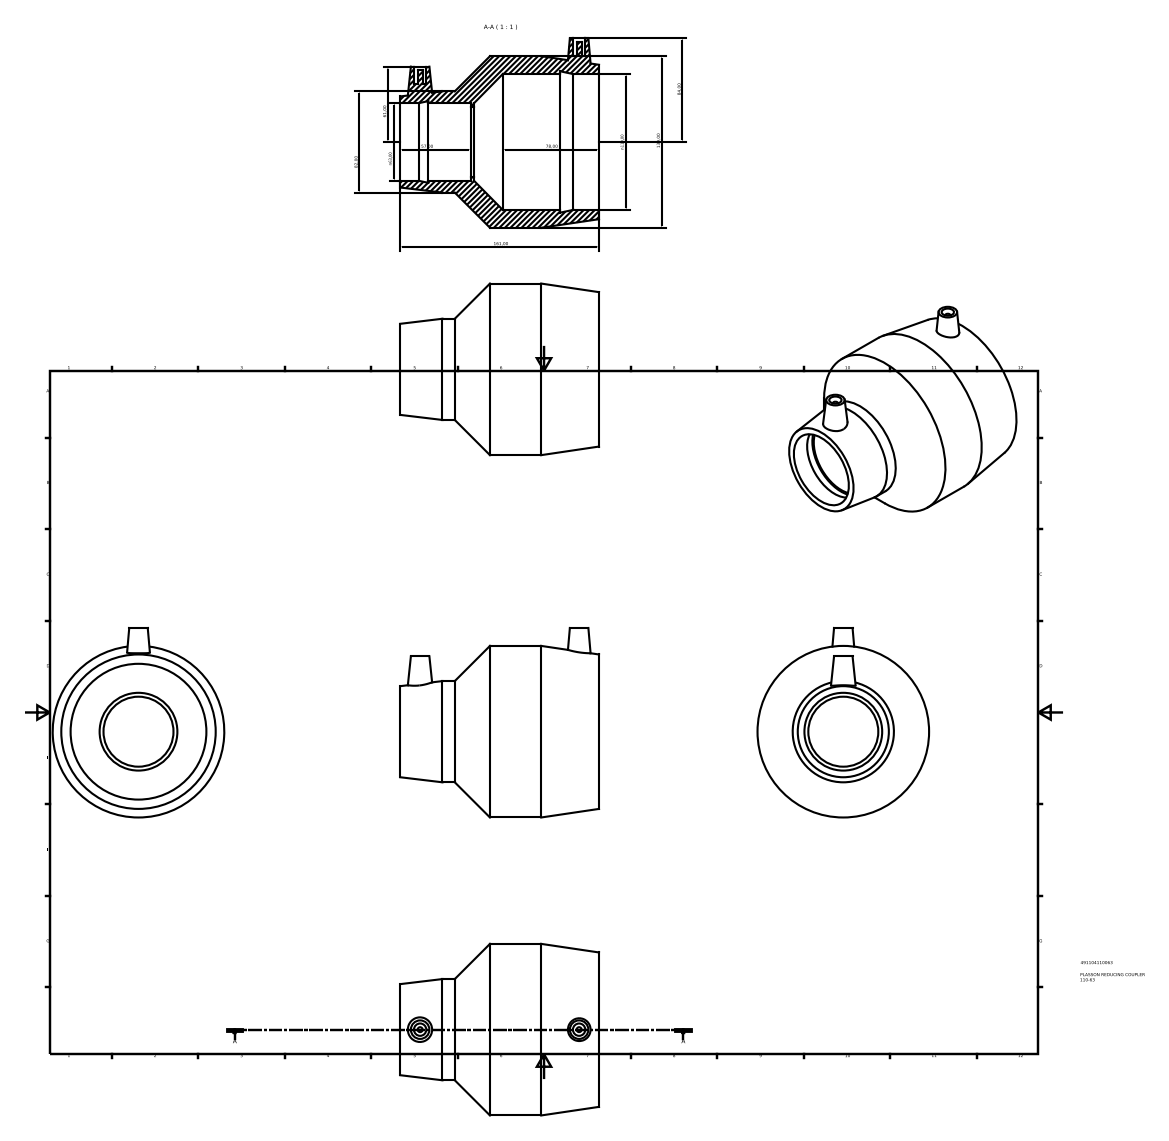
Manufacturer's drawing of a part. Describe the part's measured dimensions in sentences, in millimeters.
The part is named "491104110063". Its 3-D file was written by "Autodesk Inventor 2015 (AUTOMOTIVE_DESIGN)". It is 1 solid with 31 faces: 12 planar, 11 cylindrical and 8 other. Overall it measures 161 by 153.5 by 139 millimeters. Its volume is 703 727 cubic millimeters and its surface area 120 132 square millimeters. Round holes: 2 of diameter 10, 1 of diameter 56.7, 1 of diameter 63, 1 of diameter 110. Round bosses or shafts: 2 of diameter 4, 1 of diameter 139, 1 of diameter 82. The main face-to-face distances are 161, 129.8, 31.2, 59.85, 69.95, 101.15, 57, 2.85, 72.8, 104. The hole center spacings are 128.8.
